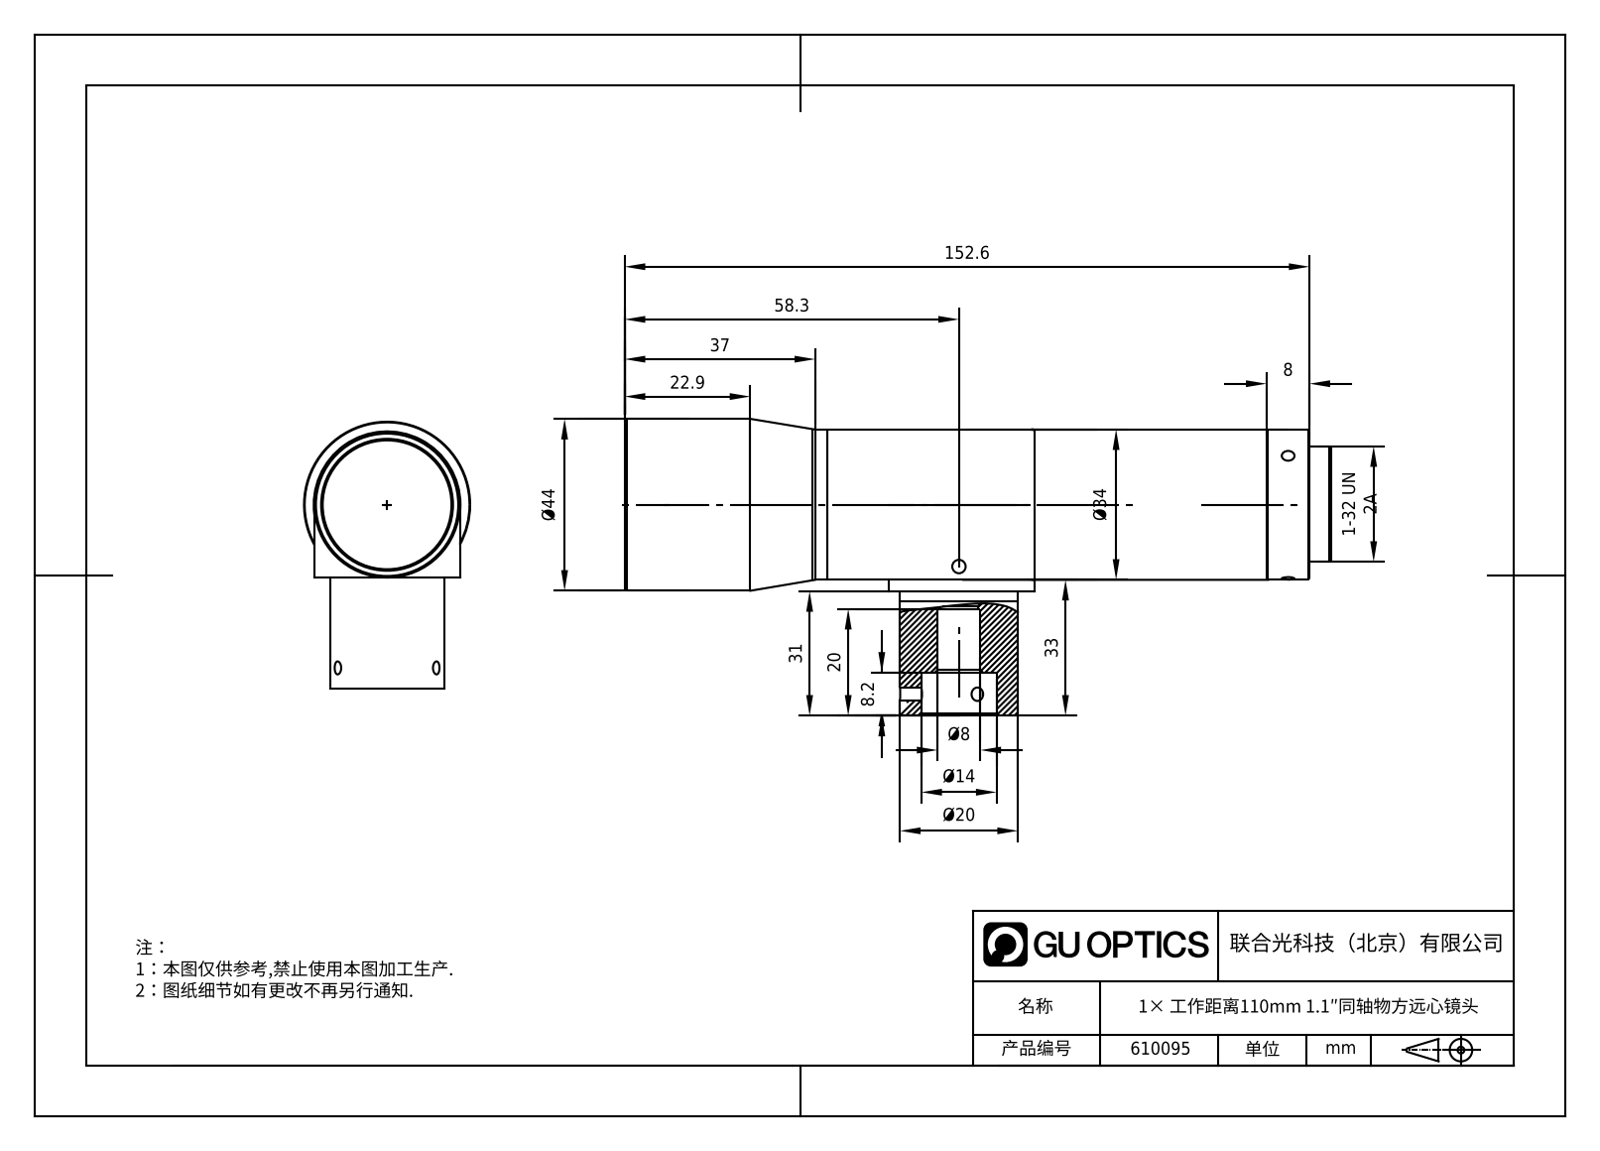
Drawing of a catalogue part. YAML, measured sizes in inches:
part_name: "WWK10-110CP-111V3"
step_written_by: "SolidWorks 2017 (CONFIG_CONTROL_DESIGN)"
units: inches
bodies: {solids: 1, faces: 173, planar: 37, cylindrical: 91, other: 45}
overall_size: [6.16, 2.835, 1.732]
volume: 9.98
surface_area: 40.2
round_holes:
  - {diameter: 0.063, count: 4}
  - {diameter: 0.091, count: 4}
  - {diameter: 0.098, count: 3}
  - {diameter: 0.106, count: 2}
  - {diameter: 0.295, count: 1}
  - {diameter: 0.315, count: 1}
  - {diameter: 0.551, count: 1}
  - {diameter: 0.598, count: 1}
  - {diameter: 0.63, count: 1}
  - {diameter: 0.65, count: 1}
  - {diameter: 0.681, count: 1}
  - {diameter: 0.695, count: 1}
round_bosses_or_shafts:
  - {diameter: 1.732, count: 1}
  - {diameter: 1.339, count: 1}
  - {diameter: 1.291, count: 1}
  - {diameter: 1, count: 1}
  - {diameter: 0.787, count: 1}
partial_cylinders:
  - {radius: 0.039, count: 4}
  - {radius: 0.059, count: 4}
  - {radius: 0.807, count: 1}
face_to_face_distances: [1.339, 5.873, 0.031, 5.904, 1.72, 4.153, 4.184, 2.665, 0.945, 3.208]
hole_center_spacings: [0.666, 0.748, 1.102, 1.332, 1.811]
